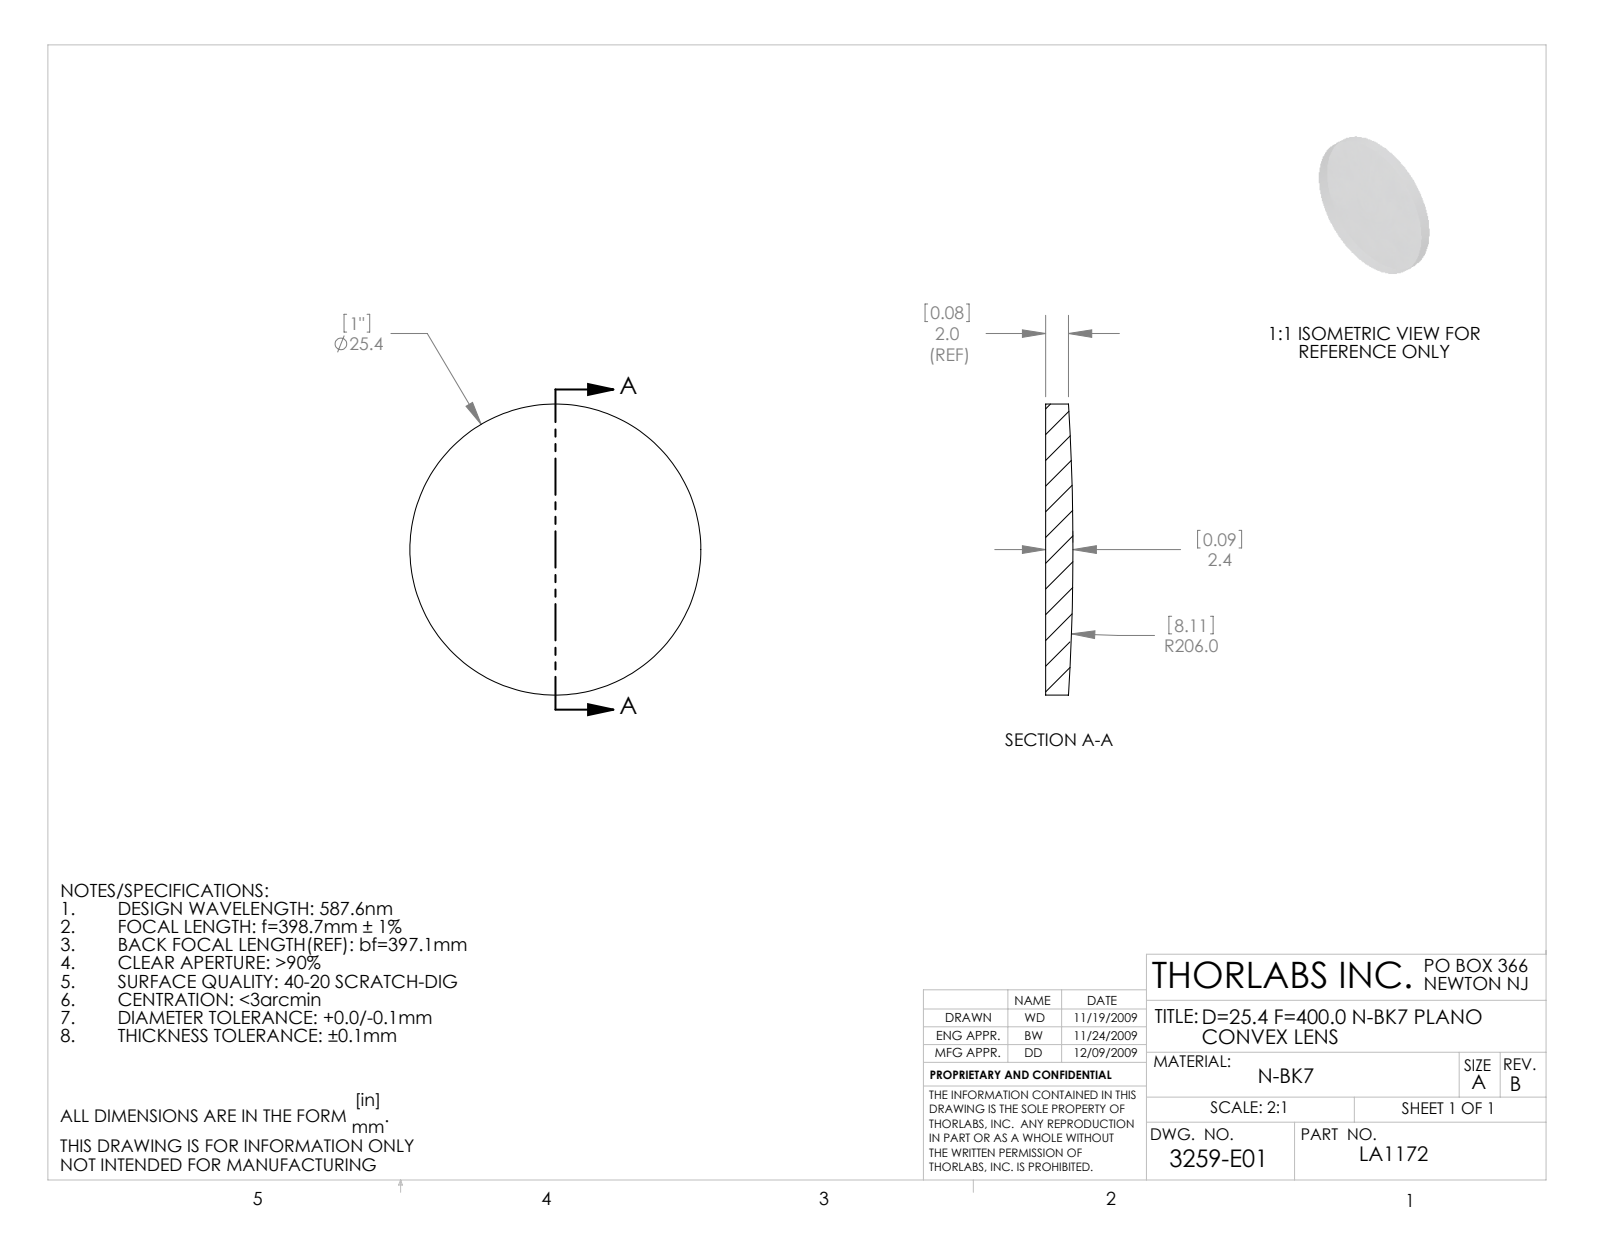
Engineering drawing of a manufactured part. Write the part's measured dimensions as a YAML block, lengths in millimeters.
part_name: "3259-E0W"
step_written_by: "SolidWorks 2009 (AUTOMOTIVE_DESIGN)"
units: millimeters
bodies: {solids: 1, faces: 5, planar: 1, cylindrical: 2, other: 2}
overall_size: [25.4, 25.4, 2.39]
volume: 1112
surface_area: 1173
round_bosses_or_shafts:
  - {diameter: 25.4, count: 1}
